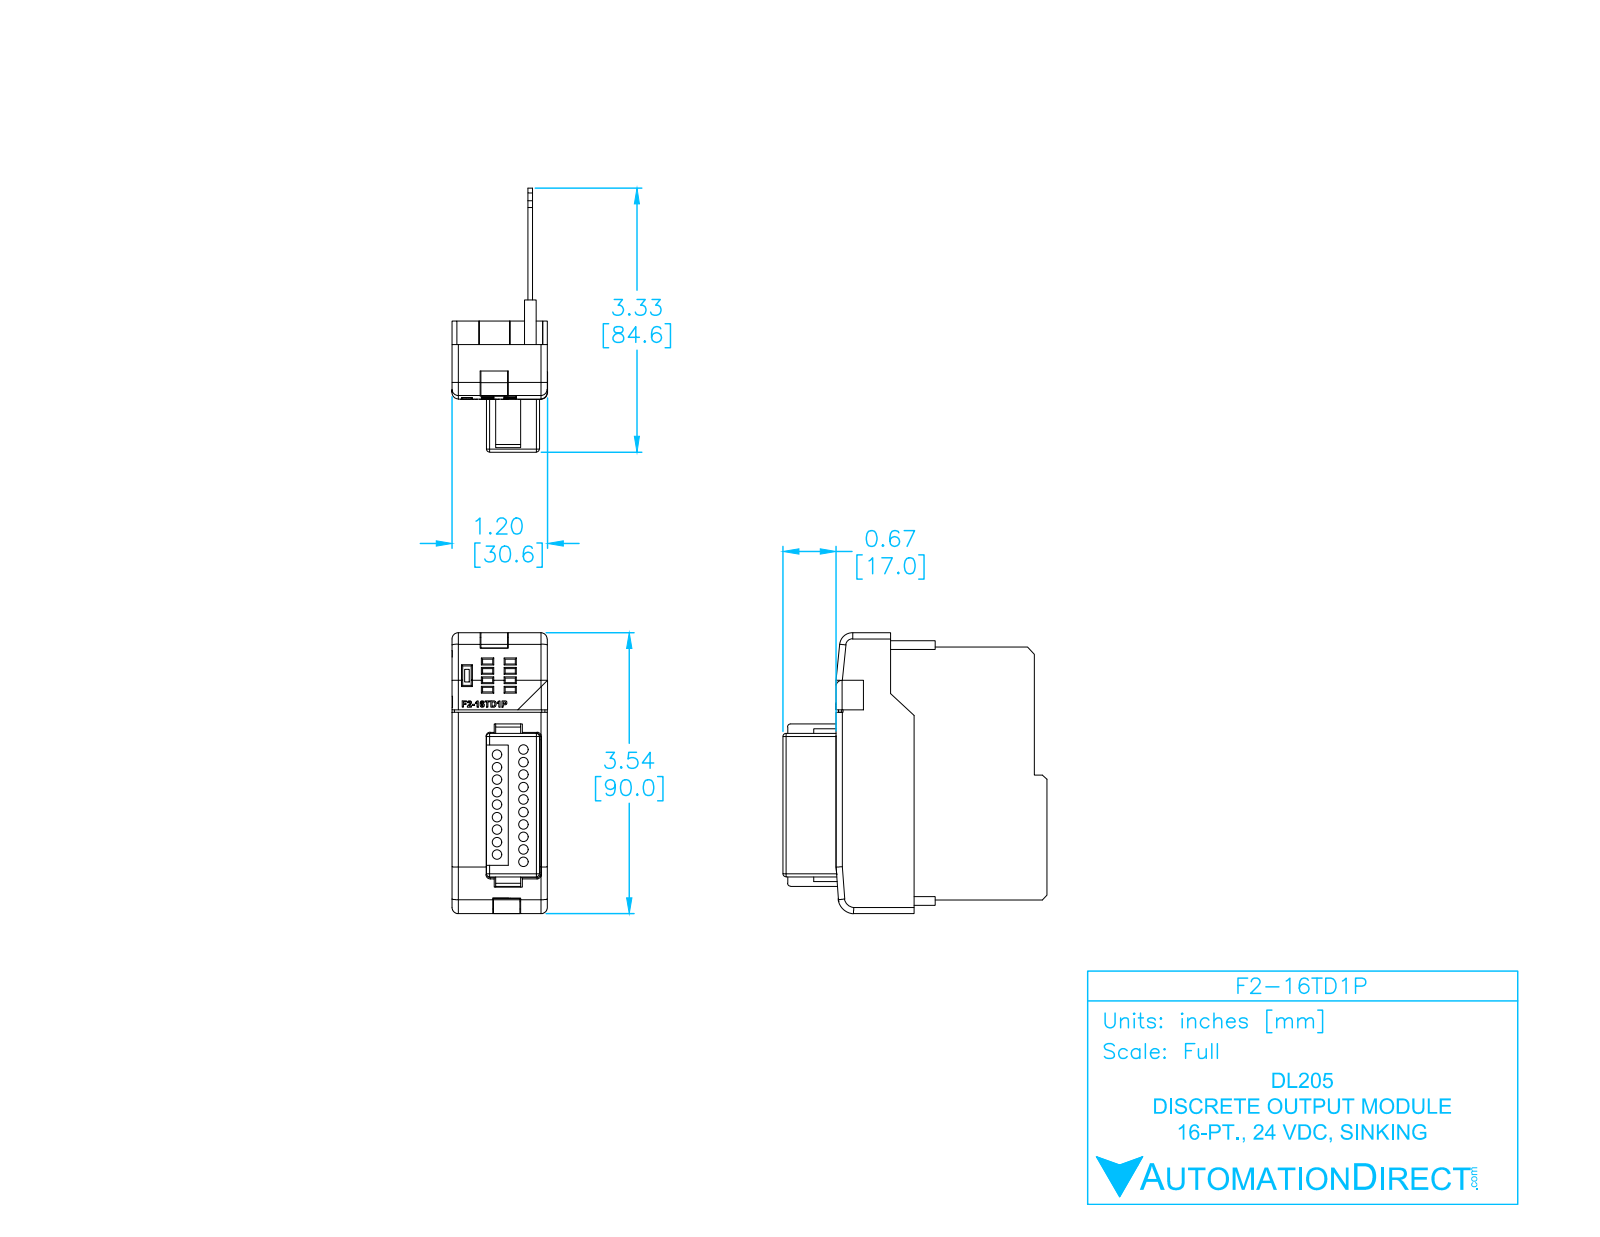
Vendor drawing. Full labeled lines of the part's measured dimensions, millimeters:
Part name (STEP PRODUCT): F2-16TD1P
STEP written by: SolidWorks 2009 (AUTOMOTIVE_DESIGN)
Units: millimetres
Bodies: 2 solids, 638 faces (419 planar, 158 cylindrical, 61 other)
Overall size (bounding box): 90 × 84.6 × 30.55
Volume: 30 556 mm³ · Surface area: 32 608 mm²
Round holes (diameter × count): ⌀3 ×19
Partial cylindrical surfaces — rounded edges, fillets, slot ends (radius × count): R0.35 ×28, R1 ×18, R0.5 ×12, R2 ×11, R0.25 ×6, R2.62 ×1, R3.79 ×1, R4.12 ×1
Main face-to-face distances: 1.5, 4.72, 3.22, 6.22, 0.5, 1, 24.28, 29, 18, 11
Hole centre spacings: 4, 8, 12, 16, 8.61, 8.77, 20, 10.16
